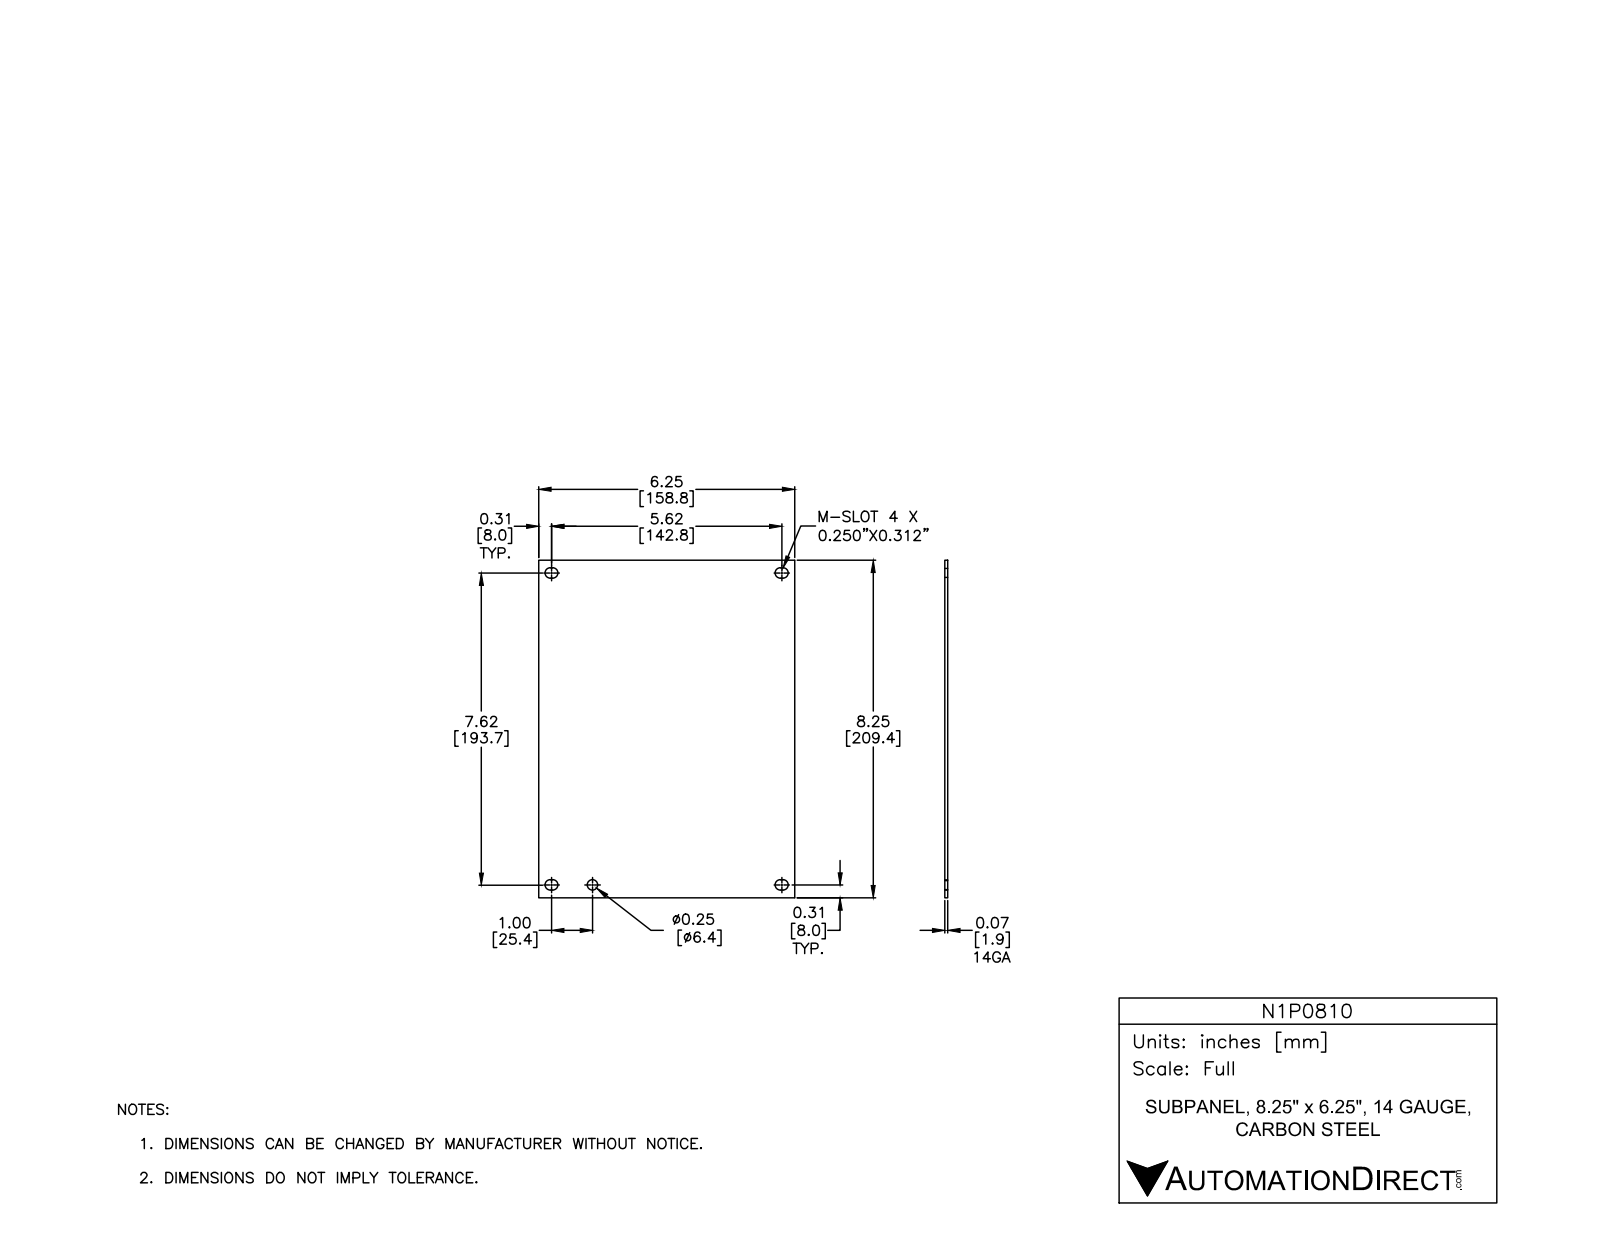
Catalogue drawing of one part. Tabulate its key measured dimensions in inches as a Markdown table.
| quantity | value |
| --- | --- |
| part name | N1P0810 |
| STEP written by | Autodesk Inventor 2012 (AUTOMOTIVE_DESIGN) |
| units | inches |
| bodies | 1 solid, 23 faces (14 planar, 9 cylindrical, 0 other) |
| overall size | 8.25 × 6.25 × 0.074 |
| volume | 3.793 in³ |
| surface area | 105 in² |
| round holes (diameter × count) | 0.25 × 1 |
| partial cylindrical surfaces (radius × count) | 0.125 × 8 |
| main face-to-face distances | 0.074, 6.25, 8.25, 0.438, 7.812, 0.188, 8.062, 0.25, 7.624, 7.874 |
